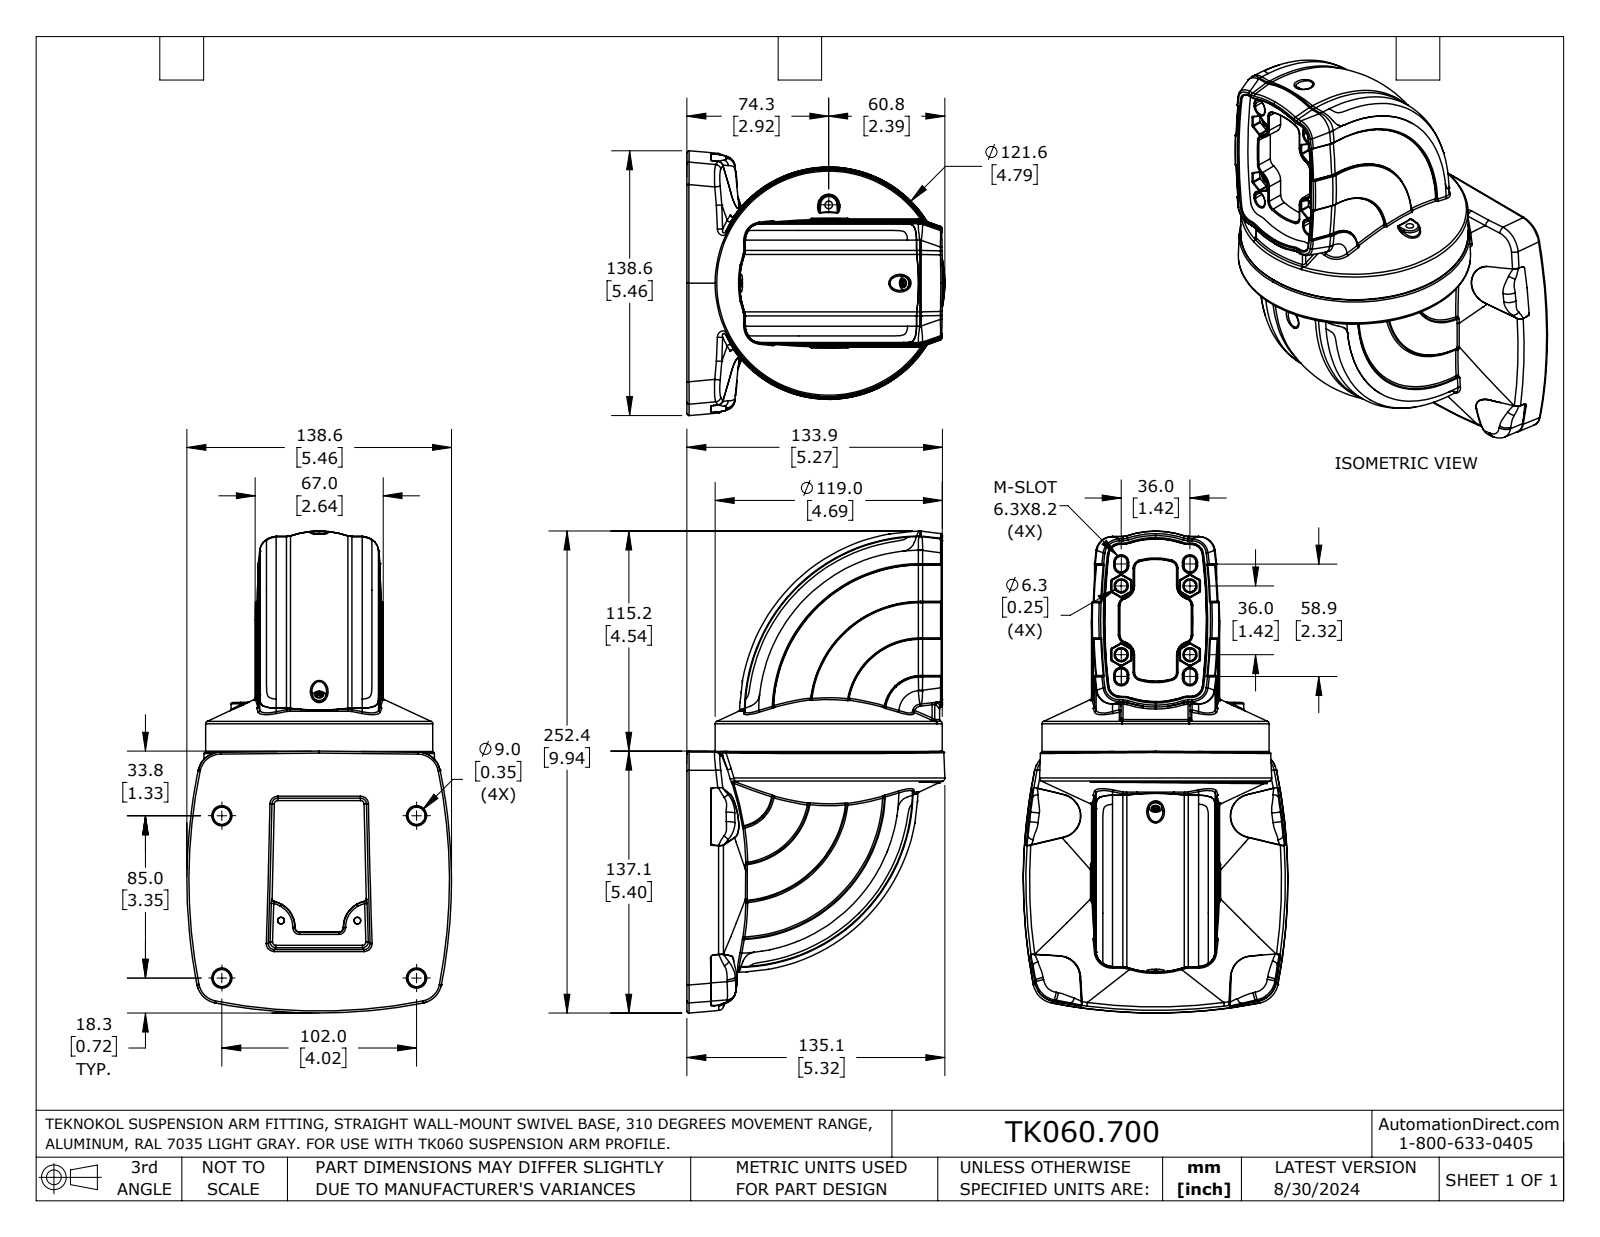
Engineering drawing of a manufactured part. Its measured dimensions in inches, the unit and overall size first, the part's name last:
Units: inches
Overall size (bounding box): 9.936 × 5.458 × 5.319
Round holes (diameter × count): ⌀0.132 ×4, ⌀0.157 ×1
Round bosses / shafts (diameter × count): ⌀0.276 ×4, ⌀0.139 ×4, ⌀4.685 ×1, ⌀0.124 ×1
Partial cylindrical surfaces — rounded edges, fillets, slot ends (radius × count): R0.02 ×28, R0.014 ×20, R0.056 ×6, R0.042 ×5, R0.039 ×4, R0.042 ×4, R0.052 ×4, R0.061 ×4
Main face-to-face distances: 1, 4.985, 3.985, 0.815, 0.185, 4.17, 4.642, 3.827, 3.642, 0.343
Hole centre spacings: 0.771, 3.83, 3.83, 4.601, 4.602, 8.431
Volume: 97.98 in³ · Surface area: 198.8 in²
Bodies: 3 solids, 1053 faces (170 planar, 140 cylindrical, 743 other)
Part name (STEP PRODUCT): TK060.700_REV1
STEP written by: SolidWorks 2023 (AUTOMOTIVE_DESIGN)
